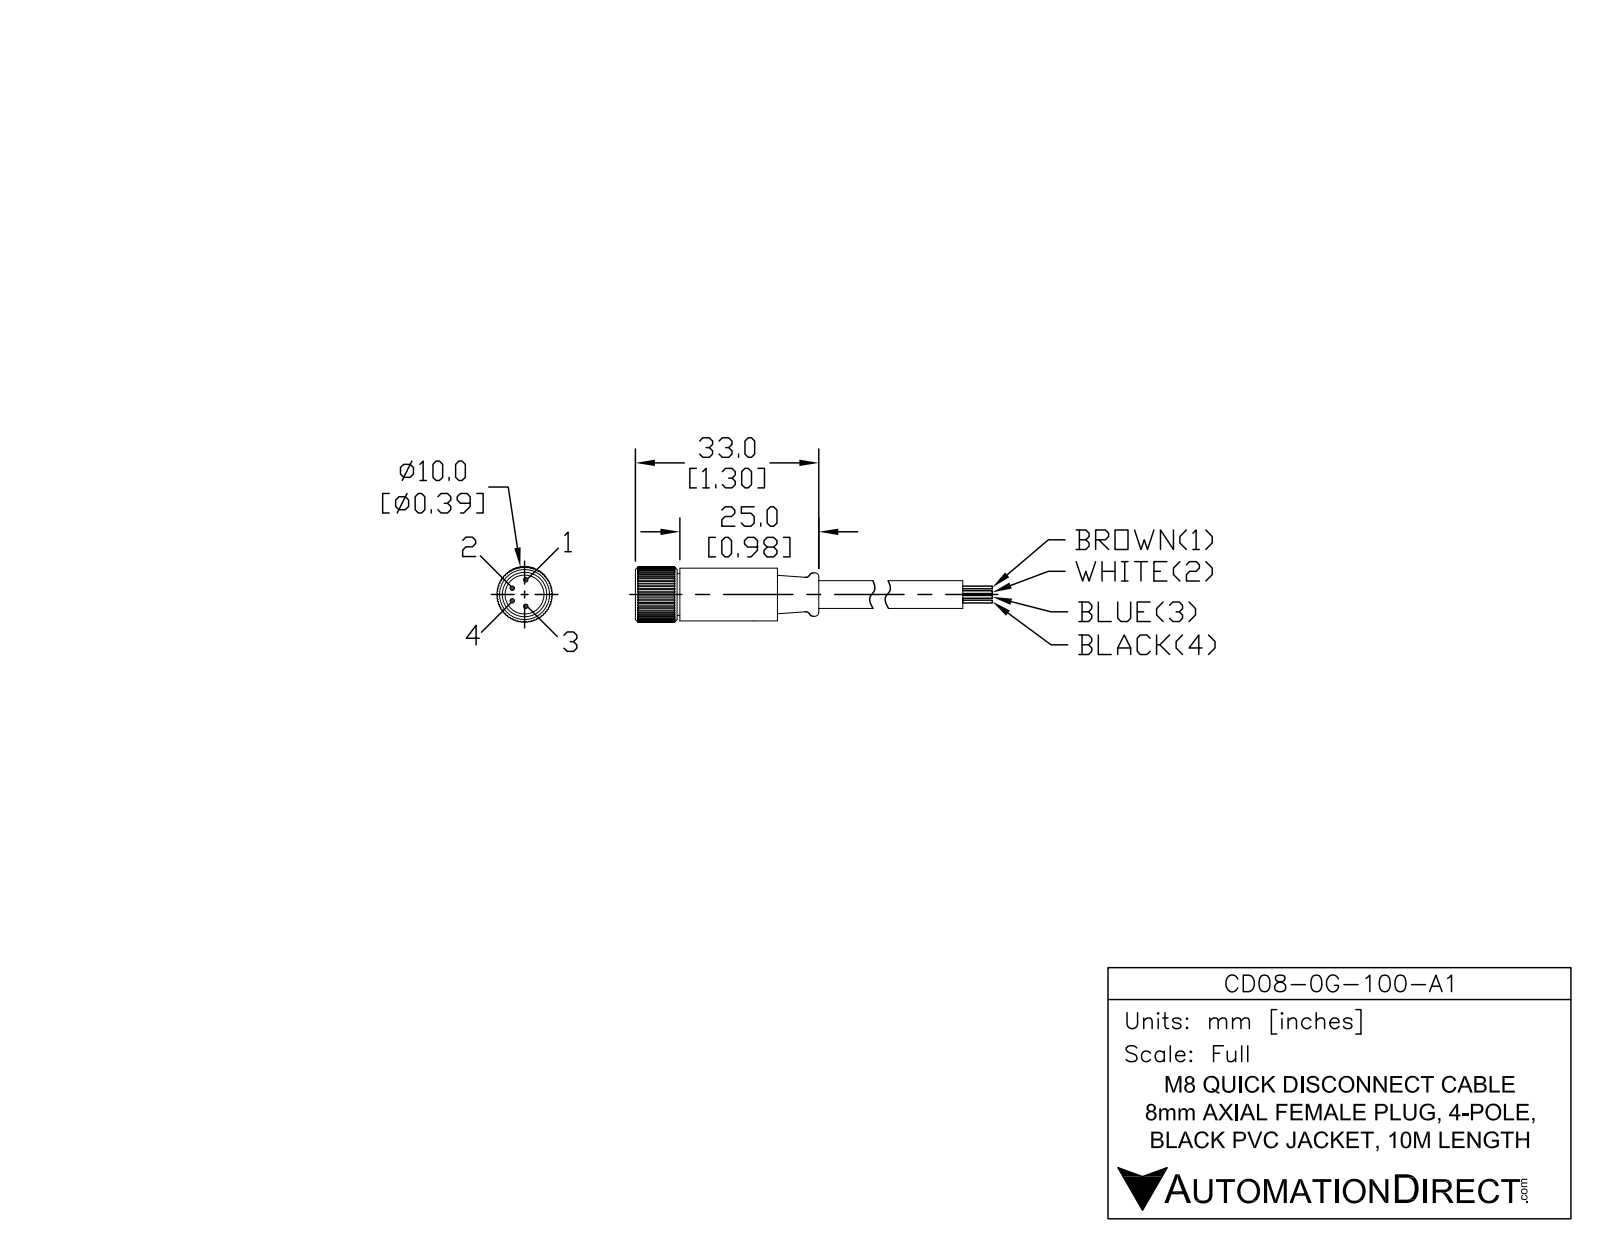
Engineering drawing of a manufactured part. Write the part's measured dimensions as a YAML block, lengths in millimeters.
part_name: "CD08-0G-100-A1"
step_written_by: "SolidWorks 2017 (AUTOMOTIVE_DESIGN)"
units: millimeters
bodies: {solids: 4, faces: 303, planar: 214, cylindrical: 85, other: 4}
overall_size: [134.6, 10, 10]
volume: 4237
surface_area: 3314
round_holes:
  - {diameter: 0.9, count: 4}
  - {diameter: 7.2, count: 1}
  - {diameter: 8, count: 1}
round_bosses_or_shafts:
  - {diameter: 10, count: 1}
  - {diameter: 7, count: 1}
  - {diameter: 4.8, count: 1}
face_to_face_distances: [26.9, 34.6, 7.7, 0.6, 9, 34, 7.1, 100, 126.9, 134]
hole_center_spacings: [2.41, 2.48, 2.71, 4.29, 2.3, 4.8]
